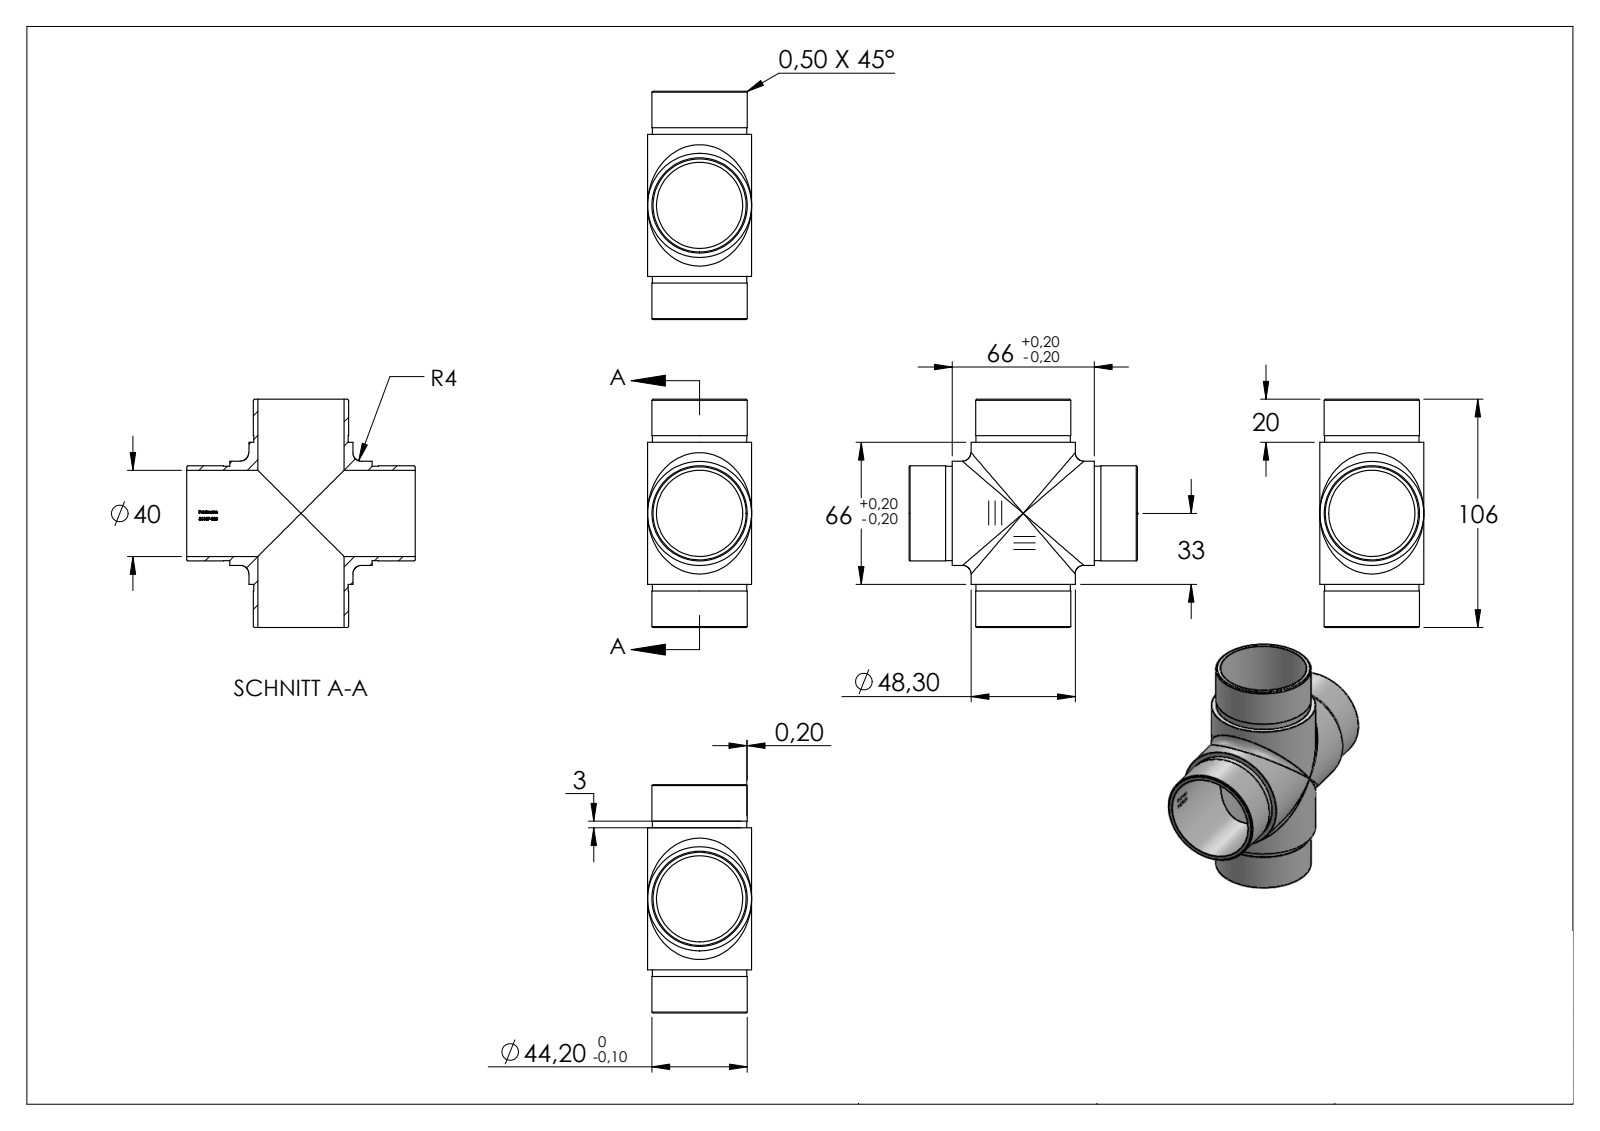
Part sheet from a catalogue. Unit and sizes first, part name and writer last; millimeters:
Units: millimetres
Overall size (bounding box): 106 × 106 × 48.3
Round holes (diameter × count): ⌀40 ×2
Round bosses / shafts (diameter × count): ⌀48.3 ×2, ⌀44.2 ×2, ⌀43.8 ×2
Partial cylindrical surfaces — rounded edges, fillets, slot ends (radius × count): R20.1 ×1
Main face-to-face distances: 20, 86, 66, 106, 17, 89, 3, 69, 72, 0.39
Volume: 65 763 mm³ · Surface area: 44 213 mm²
Bodies: 1 solid, 259 faces (100 planar, 40 cylindrical, 119 other)
Part name (STEP PRODUCT): 56187-320
STEP written by: SolidWorks 2015 (CONFIG_CONTROL_DESIGN)
